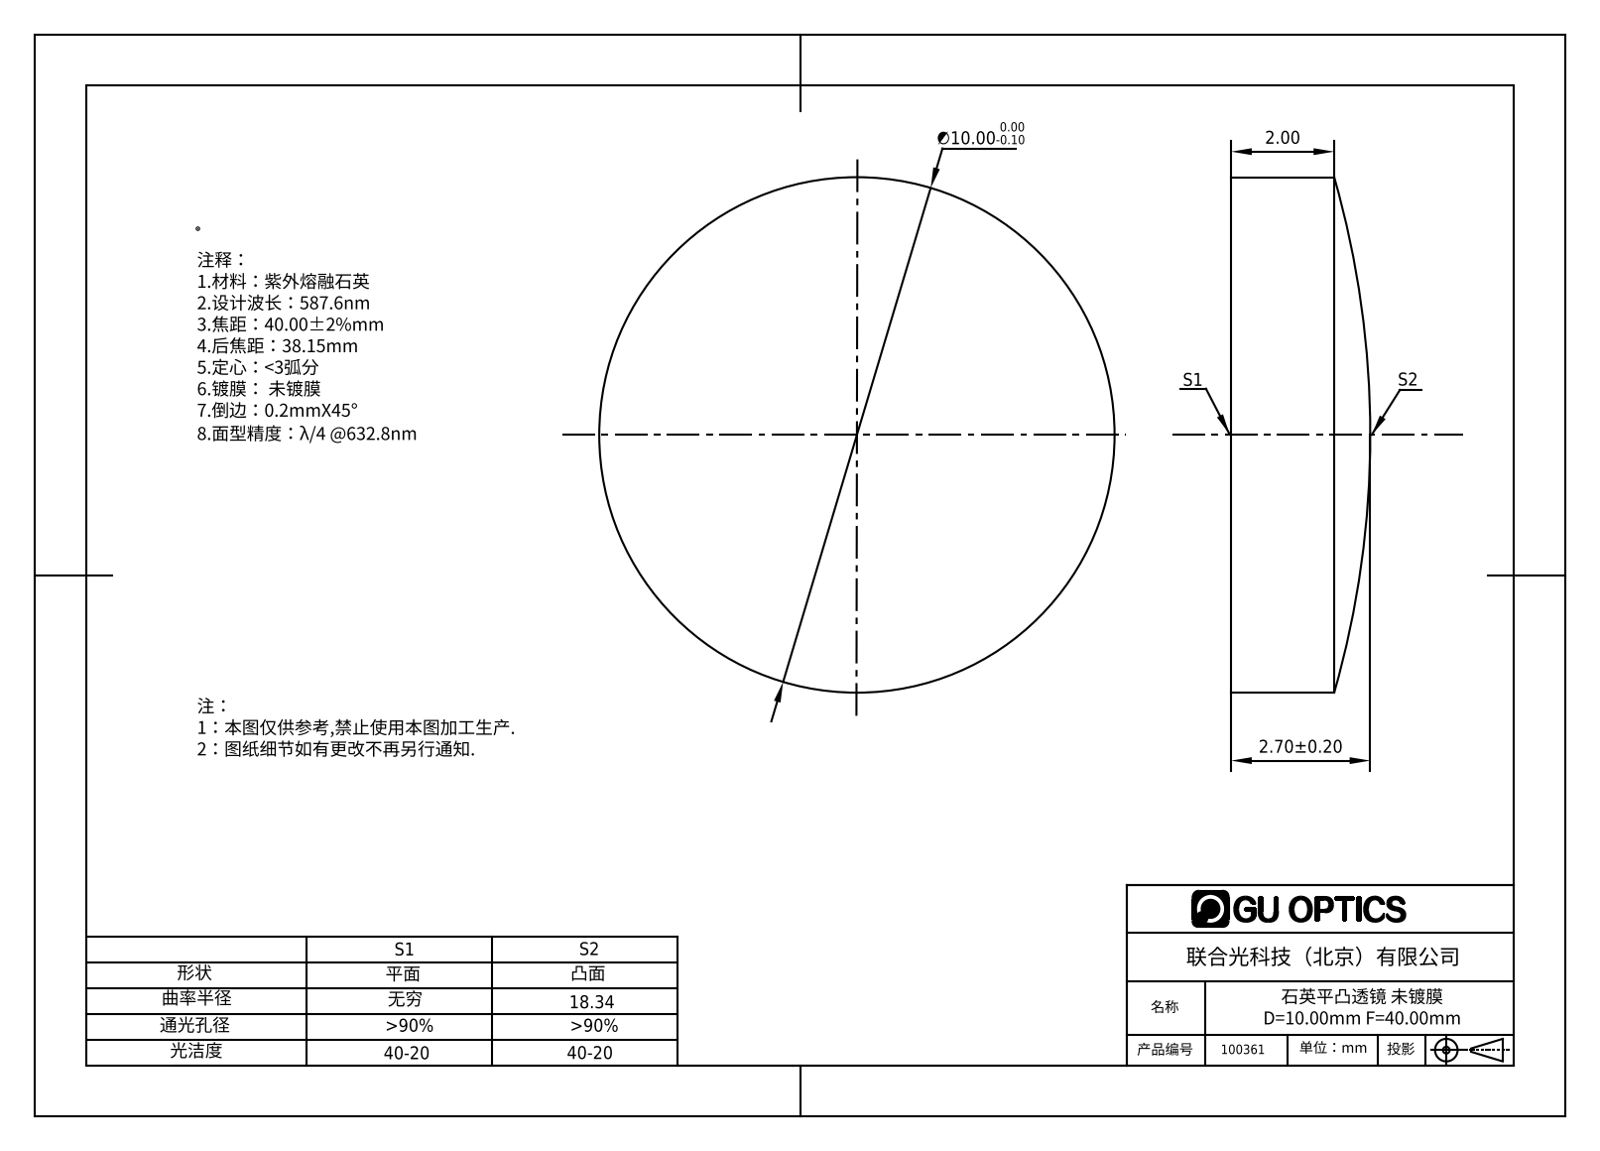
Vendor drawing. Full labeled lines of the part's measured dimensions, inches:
Part name (STEP PRODUCT): 100361
STEP written by: SolidWorks 2016 (AUTOMOTIVE_DESIGN)
Units: inches
Bodies: 1 solid, 5 faces (1 planar, 2 cylindrical, 2 other)
Overall size (bounding box): 0.394 × 0.394 × 0.106
Volume: 0.011 in³ · Surface area: 0.343 in²
Round bosses / shafts (diameter × count): ⌀0.394 ×1
